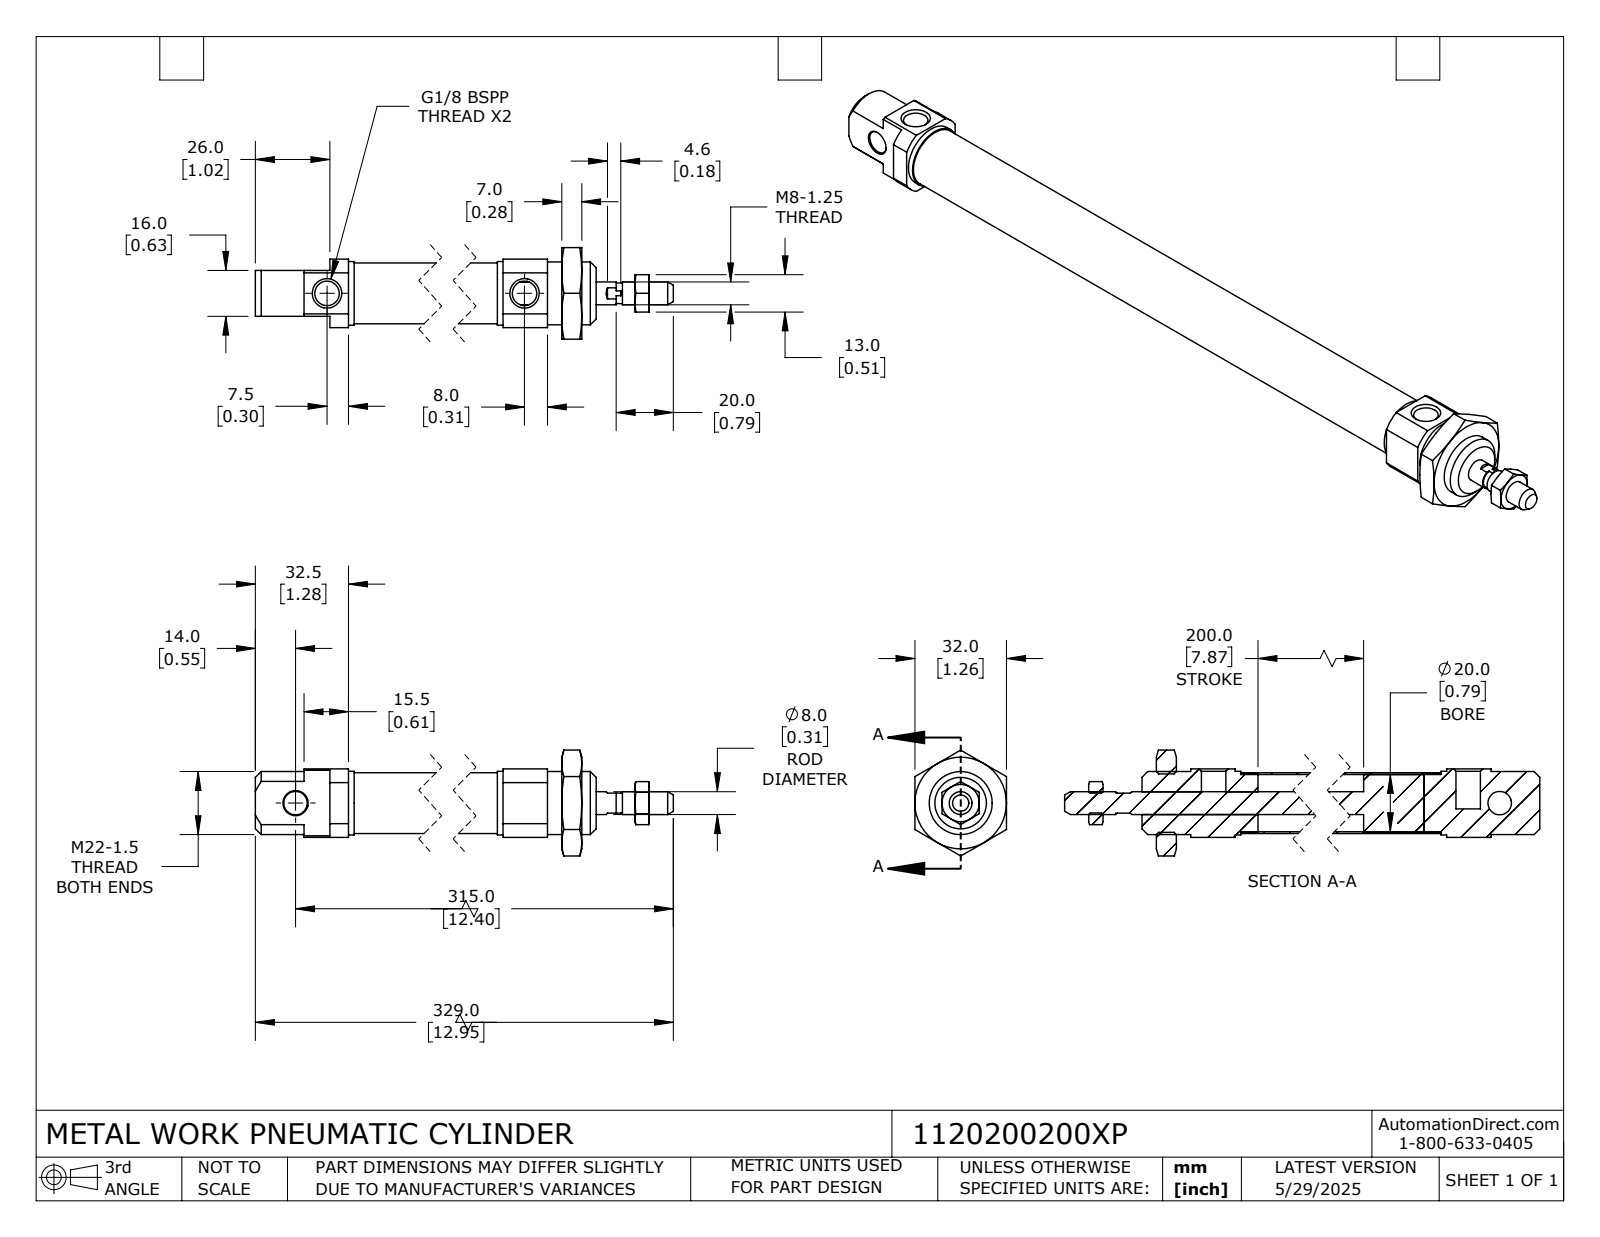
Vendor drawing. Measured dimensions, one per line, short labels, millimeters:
name: 1120200200XP; 1120200200XP_BODY; 1120200200XP_ROD
written by: SolidWorks 2024 (CONFIG_CONTROL_DESIGN)
unit: mm
bodies: 6 solids, 147 faces (56 planar, 45 cylindrical, 46 other)
size: 329 × 36.95 × 32
volume: 61 991 mm³; area: 51 319 mm²
holes: 2× ⌀8.57, 1× ⌀6.92, 1× ⌀8.2, 1× ⌀20, 1× ⌀20.38
bosses: 1× ⌀22.2, 1× ⌀22, 1× ⌀21.27, 1× ⌀20.15, 1× ⌀8, 1× ⌀7.2
rounds: 1× R13.95
face distances: 3.97, 19.97, 23.94, 8, 40.5, 261.5, 7, 5, 256.5, 249.5
hole spacings: 252
